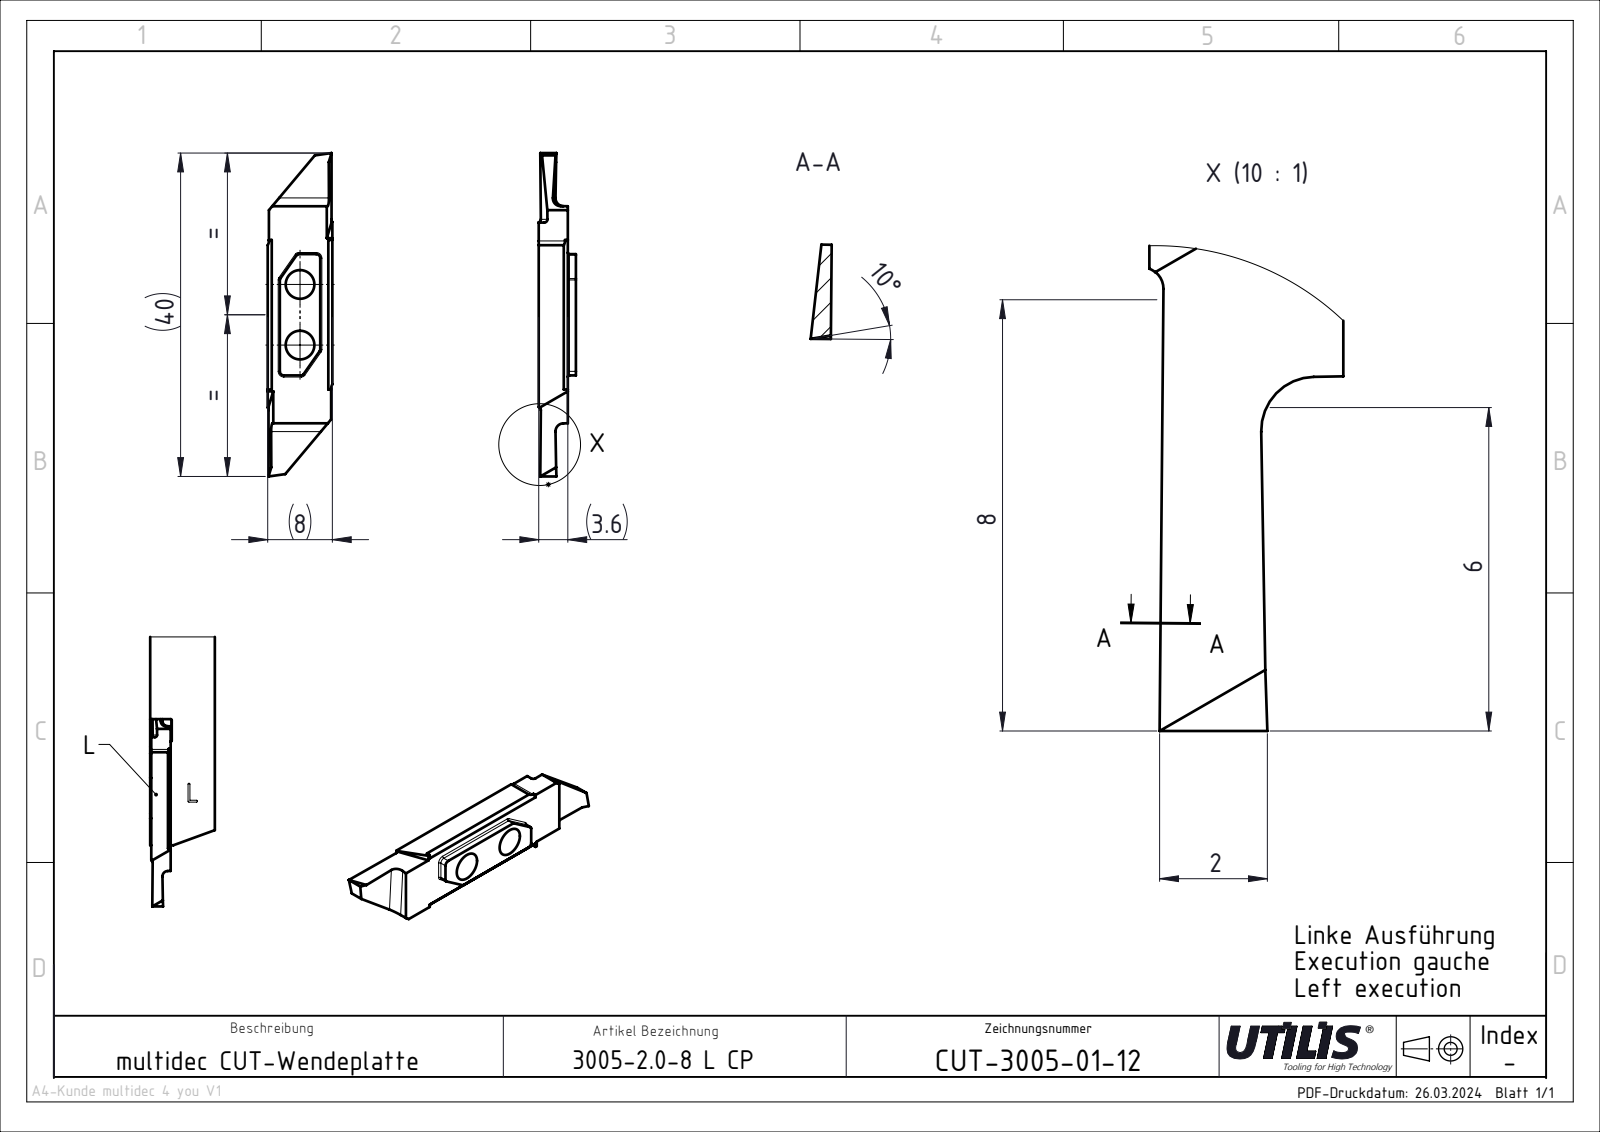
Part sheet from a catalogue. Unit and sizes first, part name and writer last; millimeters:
Units: millimetres
Overall size (bounding box): 40 × 8 × 3.6
Round holes (diameter × count): ⌀3.55 ×2
Partial cylindrical surfaces — rounded edges, fillets, slot ends (radius × count): R1 ×4, R0.4 ×2
Main face-to-face distances: 3.6, 8, 7.85, 22.54, 7.7, 40, 10.75, 29.25, 18.5
Hole centre spacings: 7.49
Volume: 804 mm³ · Surface area: 857 mm²
Bodies: 1 solid, 32 faces (22 planar, 10 cylindrical, 0 other)
Part name (STEP PRODUCT): CUT-3005 CP; ASME Y14.5
STEP written by: SolidWorks 2023 SP4 || FormatWorks Professional (AP242_MANAGED_MODEL_BASED_3D_ENGINEERING_MIM_LF)
